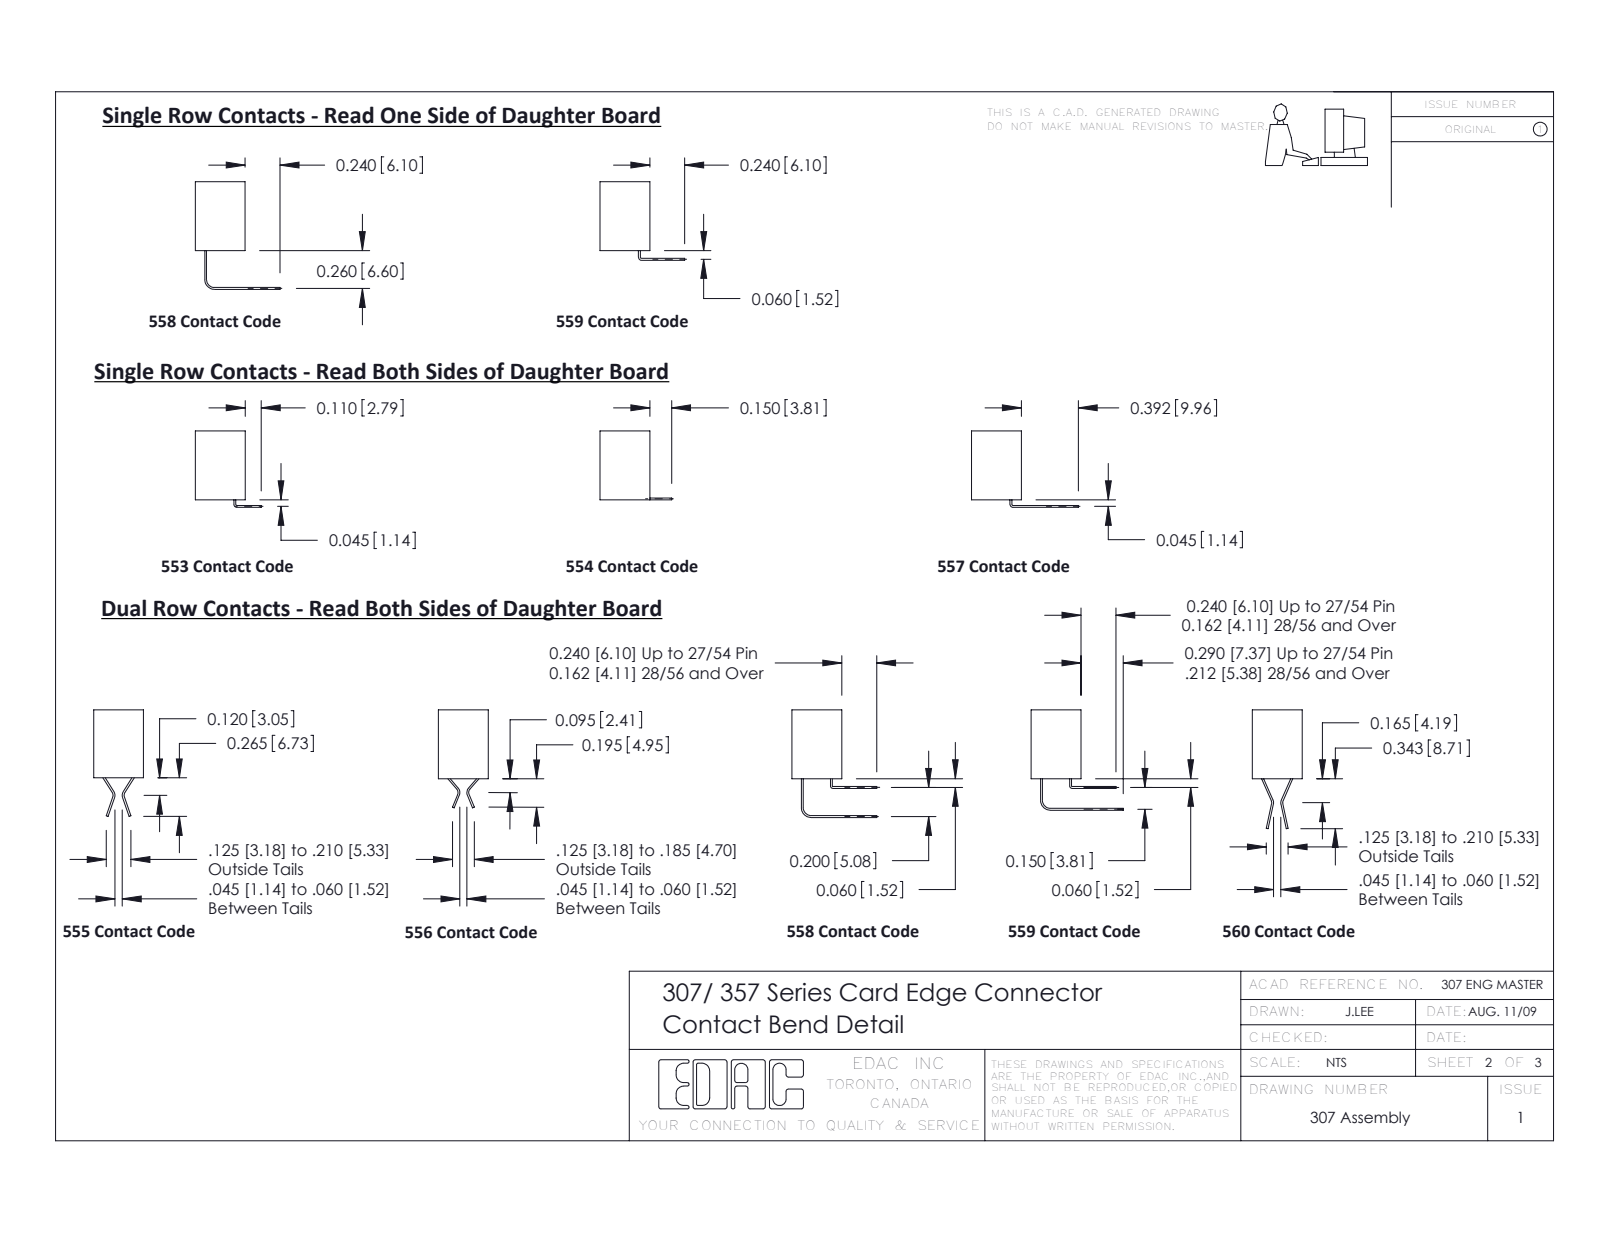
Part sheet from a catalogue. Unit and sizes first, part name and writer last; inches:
Units: inches
Overall size (bounding box): 3.732 × 3.098 × 0.343
Round holes (diameter × count): ⌀0.089 ×2, ⌀0.125 ×2, ⌀0.156 ×2
Round bosses / shafts (diameter × count): ⌀0.155 ×2
Partial cylindrical surfaces — rounded edges, fillets, slot ends (radius × count): R0.02 ×56, R0.023 ×34, R0.01 ×22, R0.03 ×16, R0.007 ×6, R0.031 ×6, R0.05 ×4, R0.026 ×3
Main face-to-face distances: 0.343, 0.013, 0.065, 0.2, 0.173, 0.265, 3.559, 0.278, 0.064, 0.078
Hole centre spacings: 3.248
Volume: 0.659 in³ · Surface area: 23.36 in²
Bodies: 39 solids, 1990 faces (1280 planar, 650 cylindrical, 60 other)
Part name (STEP PRODUCT): 307-220-068; 357-034-460-268; 307 Part_.156 Dia Mounting Holes; 307-290-001_560 (+1 more)
STEP written by: SolidWorks 2020 (CONFIG_CONTROL_DESIGN)
